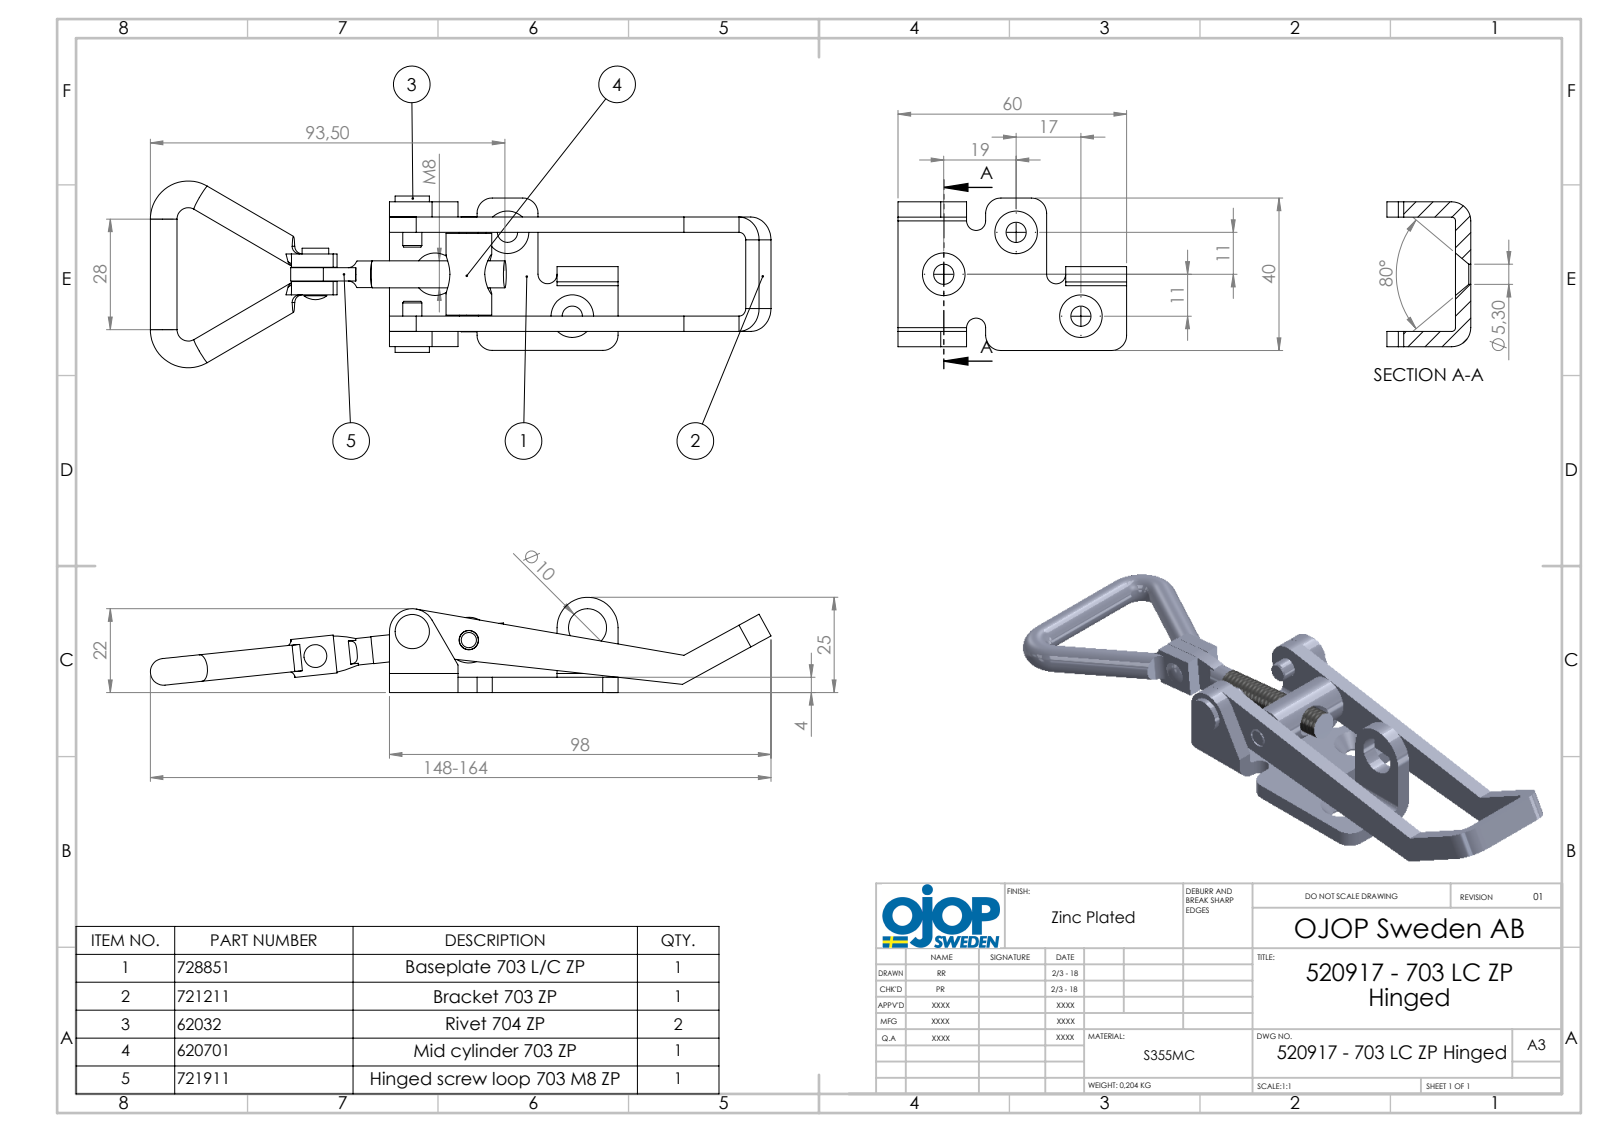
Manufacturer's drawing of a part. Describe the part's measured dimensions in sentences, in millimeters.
The part is named "703 - Ledad skruvögla; 703 - Nit ledad; 703 - Rulle; 703- Platta LC (+5 more)". Its 3-D file was written by "SolidWorks 2015 (AUTOMOTIVE_DESIGN)". It is 8 solids with 214 faces: 92 planar, 88 cylindrical and 34 other. Overall it measures 165.69 by 49 by 25 millimeters. Its volume is 27 045 cubic millimeters and its surface area 19 435 square millimeters. Round holes: 3 of diameter 5.3, 2 of diameter 5.1, 1 of diameter 4.5, 1 of diameter 7.2, 1 of diameter 7.7, 1 of diameter 10. Round bosses or shafts: 6 of diameter 7, 2 of diameter 5, 1 of diameter 12, 1 of diameter 9, 1 of diameter 7.1. Partial cylindrical surfaces (rounded edges, fillets, slot ends): 6 of radius 2, 4 of radius 4, 3 of radius 1, 3 of radius 2.5, 3 of radius 5, 3 of radius 6, 1 of radius 8. The main face-to-face distances are 4, 26, 30, 22, 17, 13, 21, 9, 8, 34. The hole center spacings are 15.01, 21.95, 27.27, 27.8, 31.33, 37.64, 41.53, 46.01.
